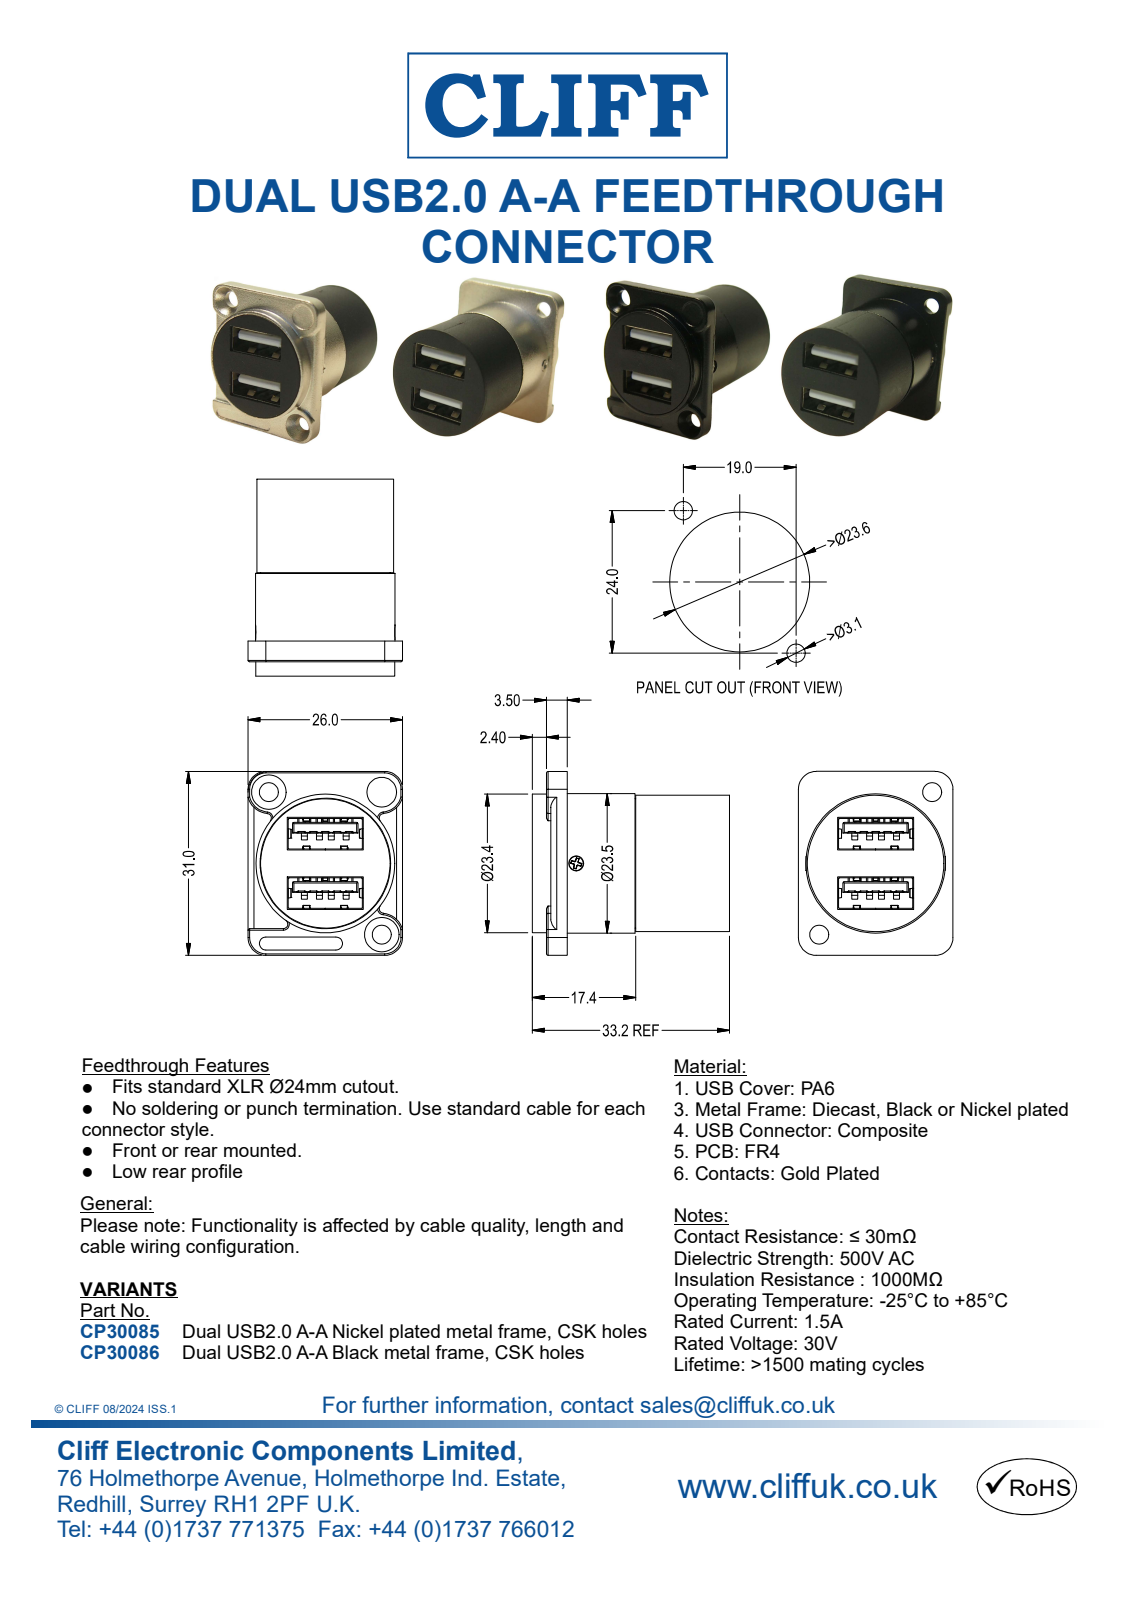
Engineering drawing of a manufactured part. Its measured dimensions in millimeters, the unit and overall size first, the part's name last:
Units: millimetres
Overall size (bounding box): 33.2 × 31 × 26
Round holes (diameter × count): ⌀3.2 ×2, ⌀2.5 ×1, ⌀5 ×1, ⌀22 ×1
Round bosses / shafts (diameter × count): ⌀23.5 ×1, ⌀23.4 ×1, ⌀23 ×1, ⌀21.8 ×1, ⌀2.4 ×1, ⌀1.5 ×1
Partial cylindrical surfaces — rounded edges, fillets, slot ends (radius × count): R0.1 ×156, R0.31 ×20, R0.5 ×20, R0.3 ×16, R0.2 ×12, R0.61 ×12, R0.25 ×10, R0.4 ×8
Main face-to-face distances: 10, 5.42, 1.8, 5.86, 0.95, 10.14, 15.86, 13.76, 5.72, 2.67
Hole centre spacings: 15.31, 19, 24, 30.61
Volume: 9 335 mm³ · Surface area: 16 033 mm²
Bodies: 2 solids, 2798 faces (2109 planar, 671 cylindrical, 18 other)
STEP written by: Autodesk Inventor 2022 (AUTOMOTIVE_DESIGN)
